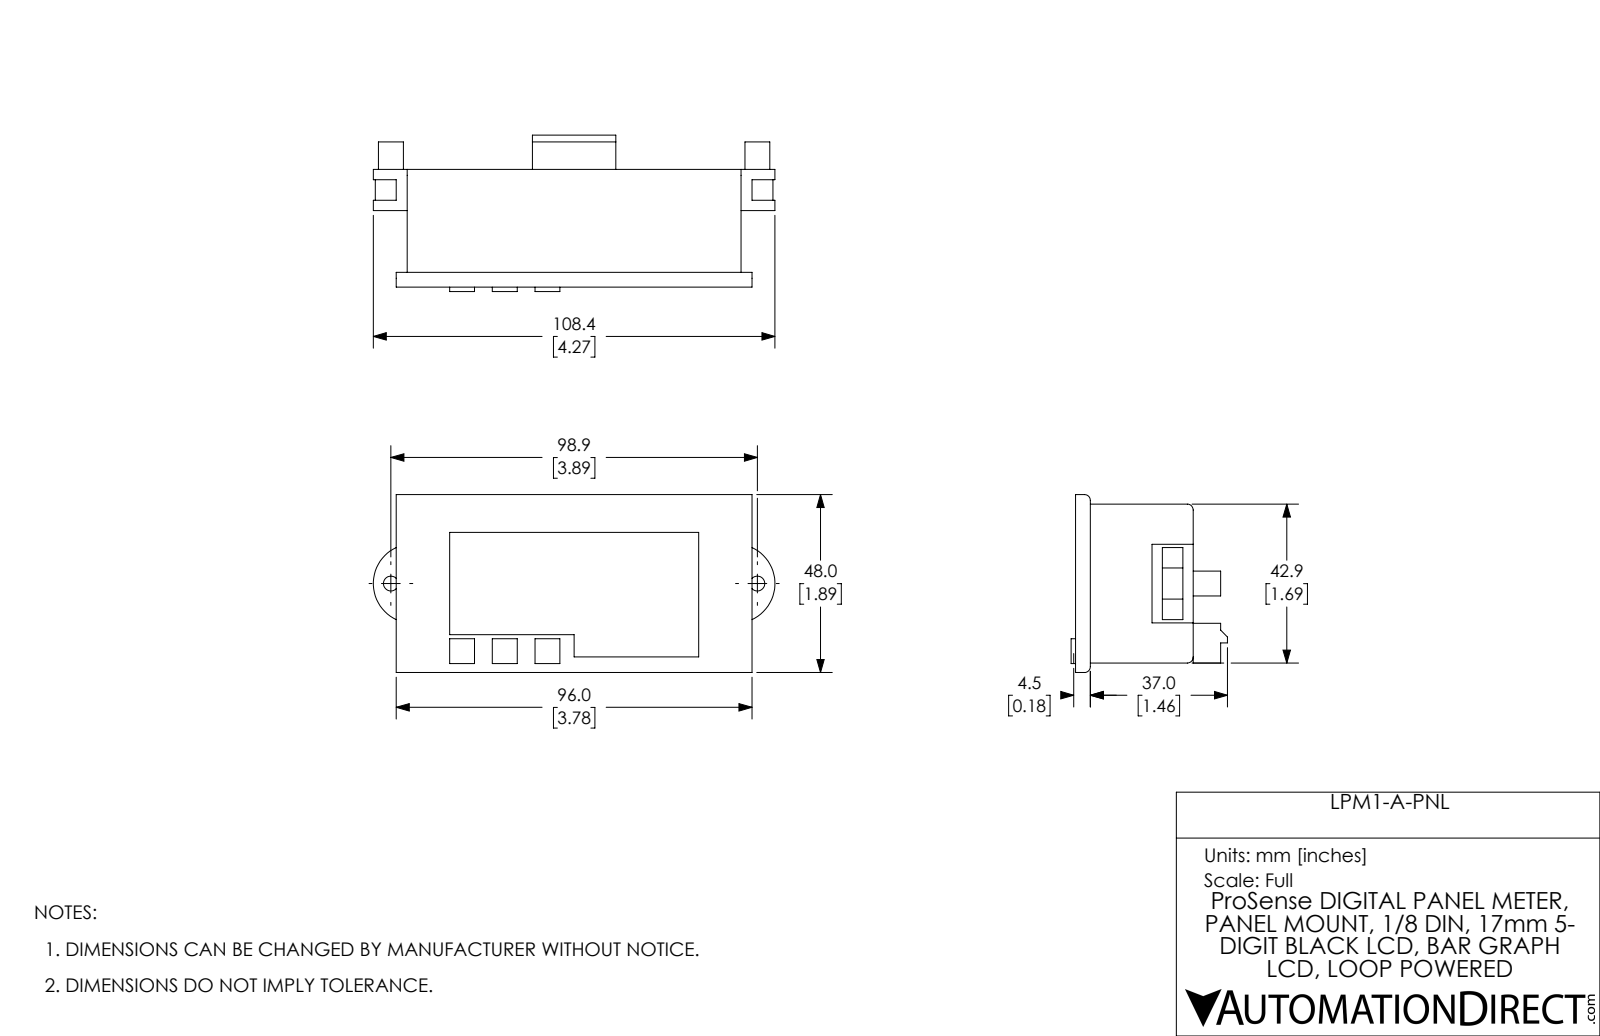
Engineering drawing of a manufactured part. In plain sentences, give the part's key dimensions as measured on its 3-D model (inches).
The part is named "LPM1-A-PNL". Its 3-D file was written by "SolidWorks 2017 (AUTOMOTIVE_DESIGN)". It is 1 solid with 77 faces: 57 planar, 20 cylindrical and 0 other. Overall it measures 4.268 by 1.89 by 1.661 inches. Its volume is 7.81 cubic inches and its surface area 31.11 square inches. Round holes: 2 of diameter 0.157. Round bosses or shafts: 2 of diameter 0.265. Partial cylindrical surfaces (rounded edges, fillets, slot ends): 4 of radius 0.063, 2 of radius 0.165, 2 of radius 0.422. The main face-to-face distances are 1.25, 1.688, 0.047, 1.203, 3.547, 0.116, 3.663, 1.093, 0.11, 0.157. The hole center spacings are 3.894.
